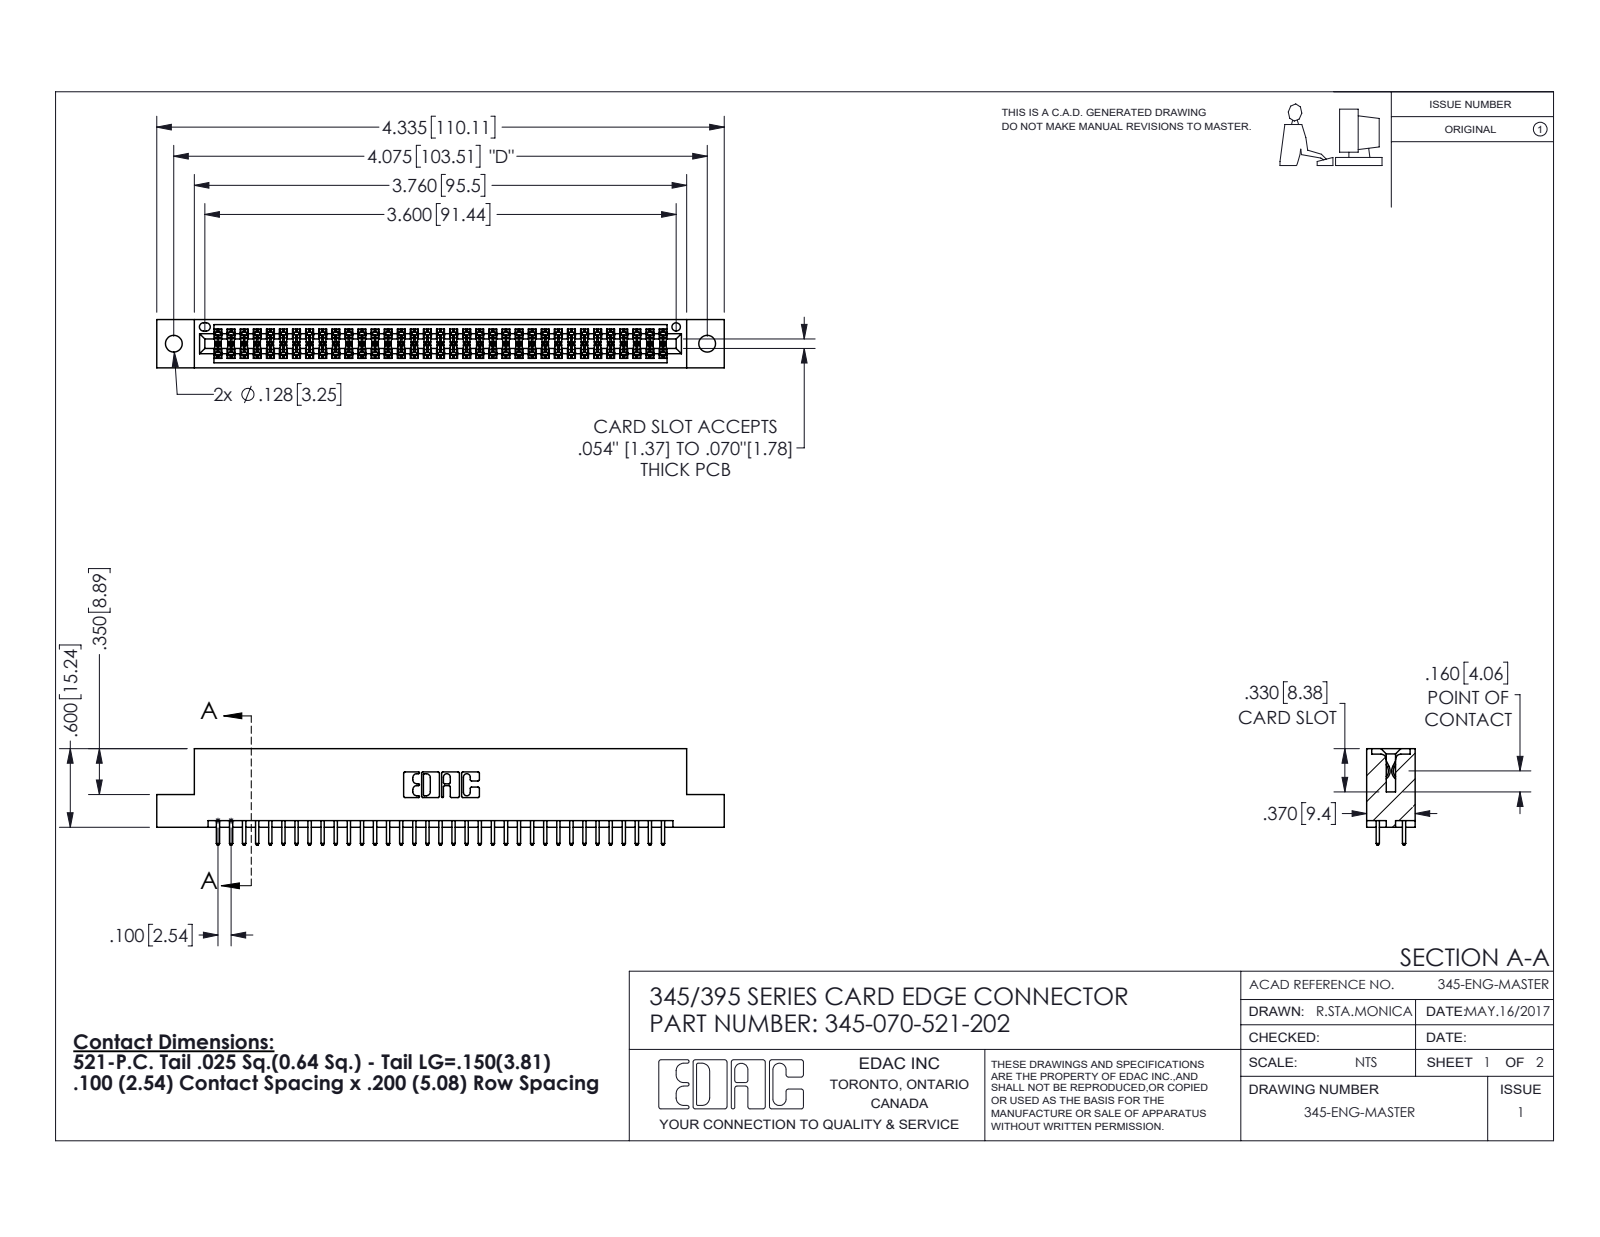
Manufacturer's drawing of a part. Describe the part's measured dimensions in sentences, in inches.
The part is named "345-292-001_345-293-121; 345 Part_Flush Mounting Lugs - 0.128 Dia; 345-070-521-202". Its 3-D file was written by "SolidWorks 2016 (CONFIG_CONTROL_DESIGN)". It is 71 solids with 3626 faces: 2390 planar, 1236 cylindrical and 0 other. Overall it measures 4.335 by 0.737 by 0.37 inches. Its volume is 0.645 cubic inches and its surface area 23.29 square inches. Round holes: 2 of diameter 0.128, 1 of diameter 0.064. Partial cylindrical surfaces (rounded edges, fillets, slot ends): 105 of radius 0.006, 70 of radius 0.01, 22 of radius 0.01, 6 of radius 0.007, 6 of radius 0.031, 3 of radius 0.026, 2 of radius 0.014, 2 of radius 0.019. The main face-to-face distances are 0.298, 0.072, 0.2, 0.37, 0.098, 0.272, 0.025, 0.225, 0.175, 0.149. The hole center spacings are 0.27, 3.839, 4.075.
